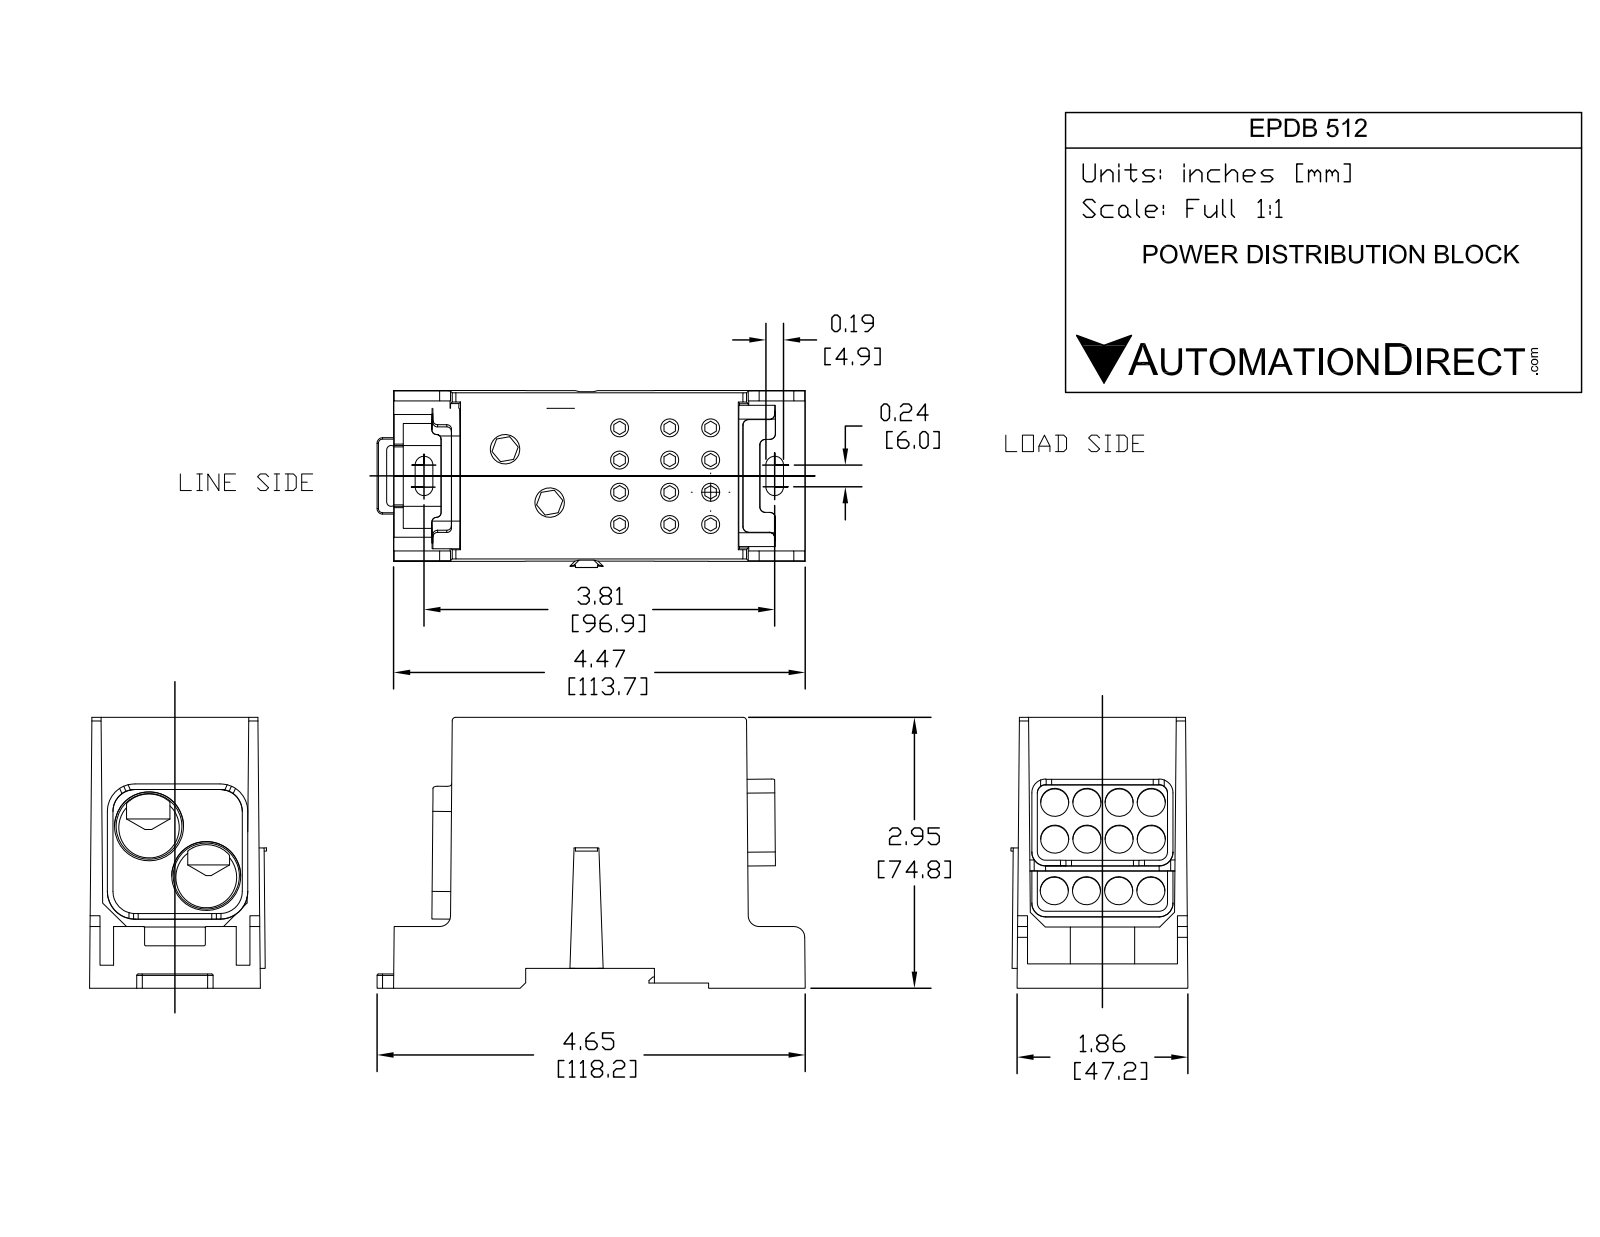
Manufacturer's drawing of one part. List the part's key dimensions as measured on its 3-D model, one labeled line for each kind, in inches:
Part name (STEP PRODUCT): EPDB512
STEP written by: SolidWorks 2011 (CONFIG_CONTROL_DESIGN)
Units: inches
Bodies: 1 solid, 418 faces (273 planar, 131 cylindrical, 14 other)
Overall size (bounding box): 4.655 × 2.945 × 1.924
Volume: 14.7 in³ · Surface area: 80.21 in²
Round holes (diameter × count): ⌀0.305 ×12, ⌀0.195 ×8, ⌀0.195 ×4, ⌀0.32 ×2, ⌀0.75 ×2
Round bosses / shafts (diameter × count): ⌀0.473 ×1, ⌀0.455 ×1
Partial cylindrical surfaces — rounded edges, fillets, slot ends (radius × count): R0.06 ×10, R0.05 ×8, R0.015 ×7, R0.09 ×6, R0.15 ×6, R0.118 ×5, R0.096 ×4, R0.24 ×4
Main face-to-face distances: 2.945, 0.216, 2.729, 0.09, 0.701, 0.611, 0.06, 0.057, 0.159, 2.888
Hole centre spacings: 0.35, 0.7, 1.05, 0.531, 0.567, 0.648, 0.4, 0.445
